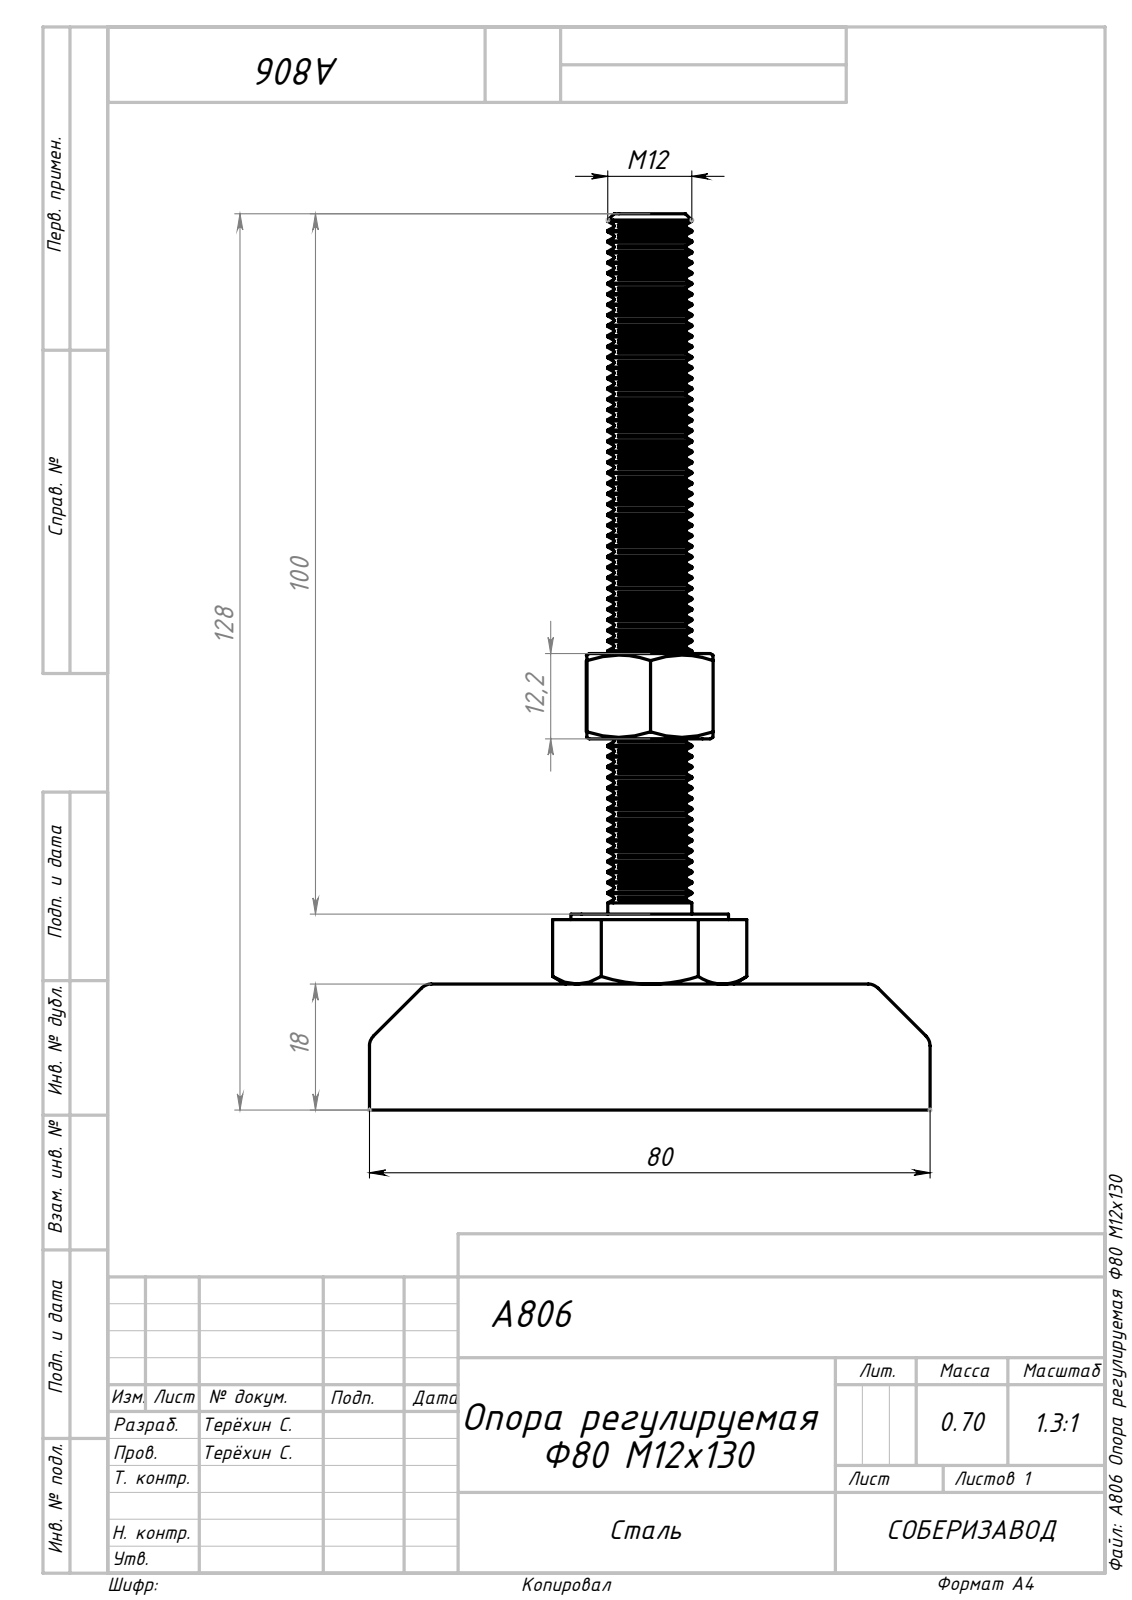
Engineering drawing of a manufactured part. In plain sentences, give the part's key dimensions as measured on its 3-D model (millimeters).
The part is named "A806 Опора регулируемая Ф80 М12х130". Its 3-D file was written by "SolidWorks 2022 (AUTOMOTIVE_DESIGN)". It is 0 solids with 653 faces: 35 planar, 128 cylindrical and 490 other. Overall it measures 128 by 80 by 80 millimeters. Round holes: 1 of diameter 74. Round bosses or shafts: 1 of diameter 80, 1 of diameter 32, 1 of diameter 22.5, 1 of diameter 12, 1 of diameter 8. The main face-to-face distances are 15, 18, 3, 25, 24, 28, 10, 53, 50, 35.
